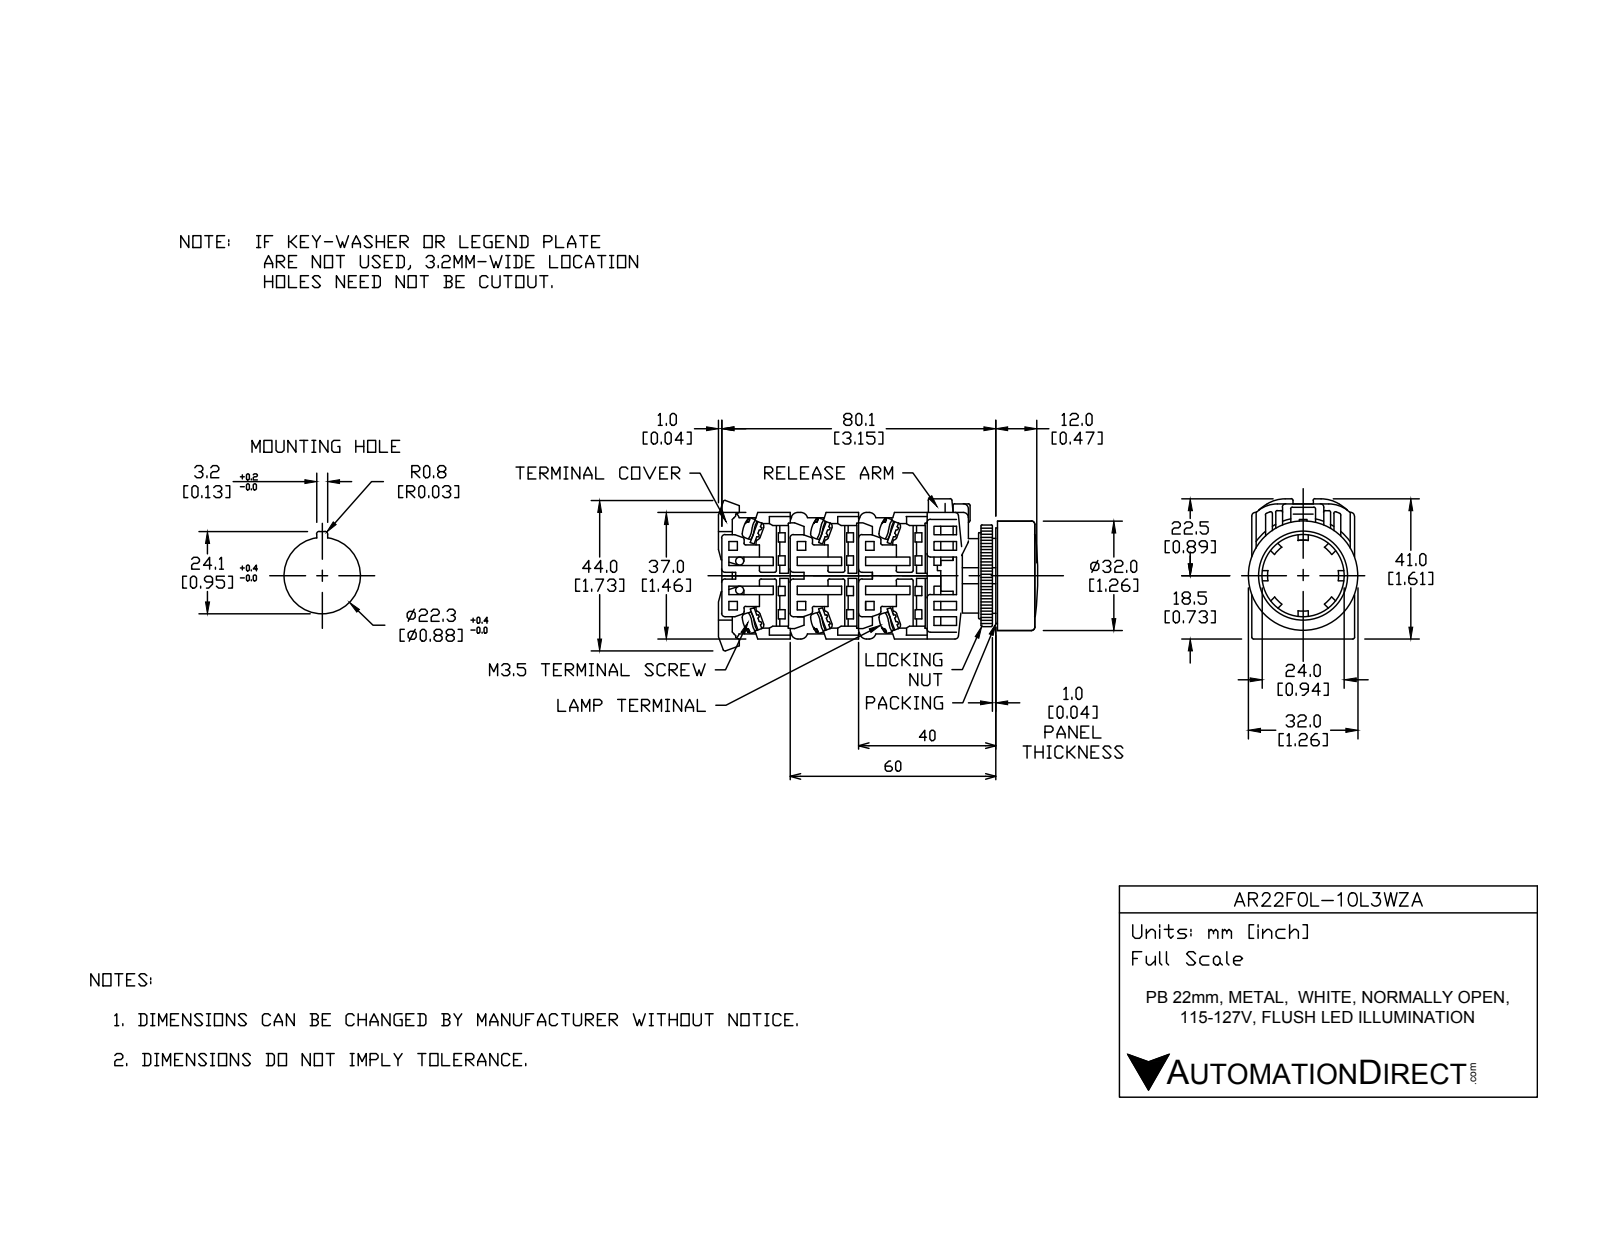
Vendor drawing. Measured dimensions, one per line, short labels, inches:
name: AR22F0L-10L3WZA
written by: SolidWorks 2017 (AUTOMOTIVE_DESIGN)
unit: in
bodies: 16 solids, 451 faces (317 planar, 99 cylindrical, 35 other)
size: 2.864 × 1.725 × 1.26
volume: 2.9 in³; area: 39.87 in²
holes: 1× ⌀0.858, 1× ⌀0.866, 1× ⌀0.984, 1× ⌀1.22
bosses: 4× ⌀0.197, 1× ⌀1.26, 1× ⌀1.201, 1× ⌀1.173, 1× ⌀0.945, 1× ⌀0.937, 1× ⌀0.856, 1× ⌀0.669
rounds: 32× R0.02, 8× R0.069, 4× R0.197, 2× R0.157, 1× R0.653, 1× R0.693
face distances: 0.039, 0.709, 1.142, 0.787, 1.122, 0.118, 0.079, 0.827, 0.014, 0.295
